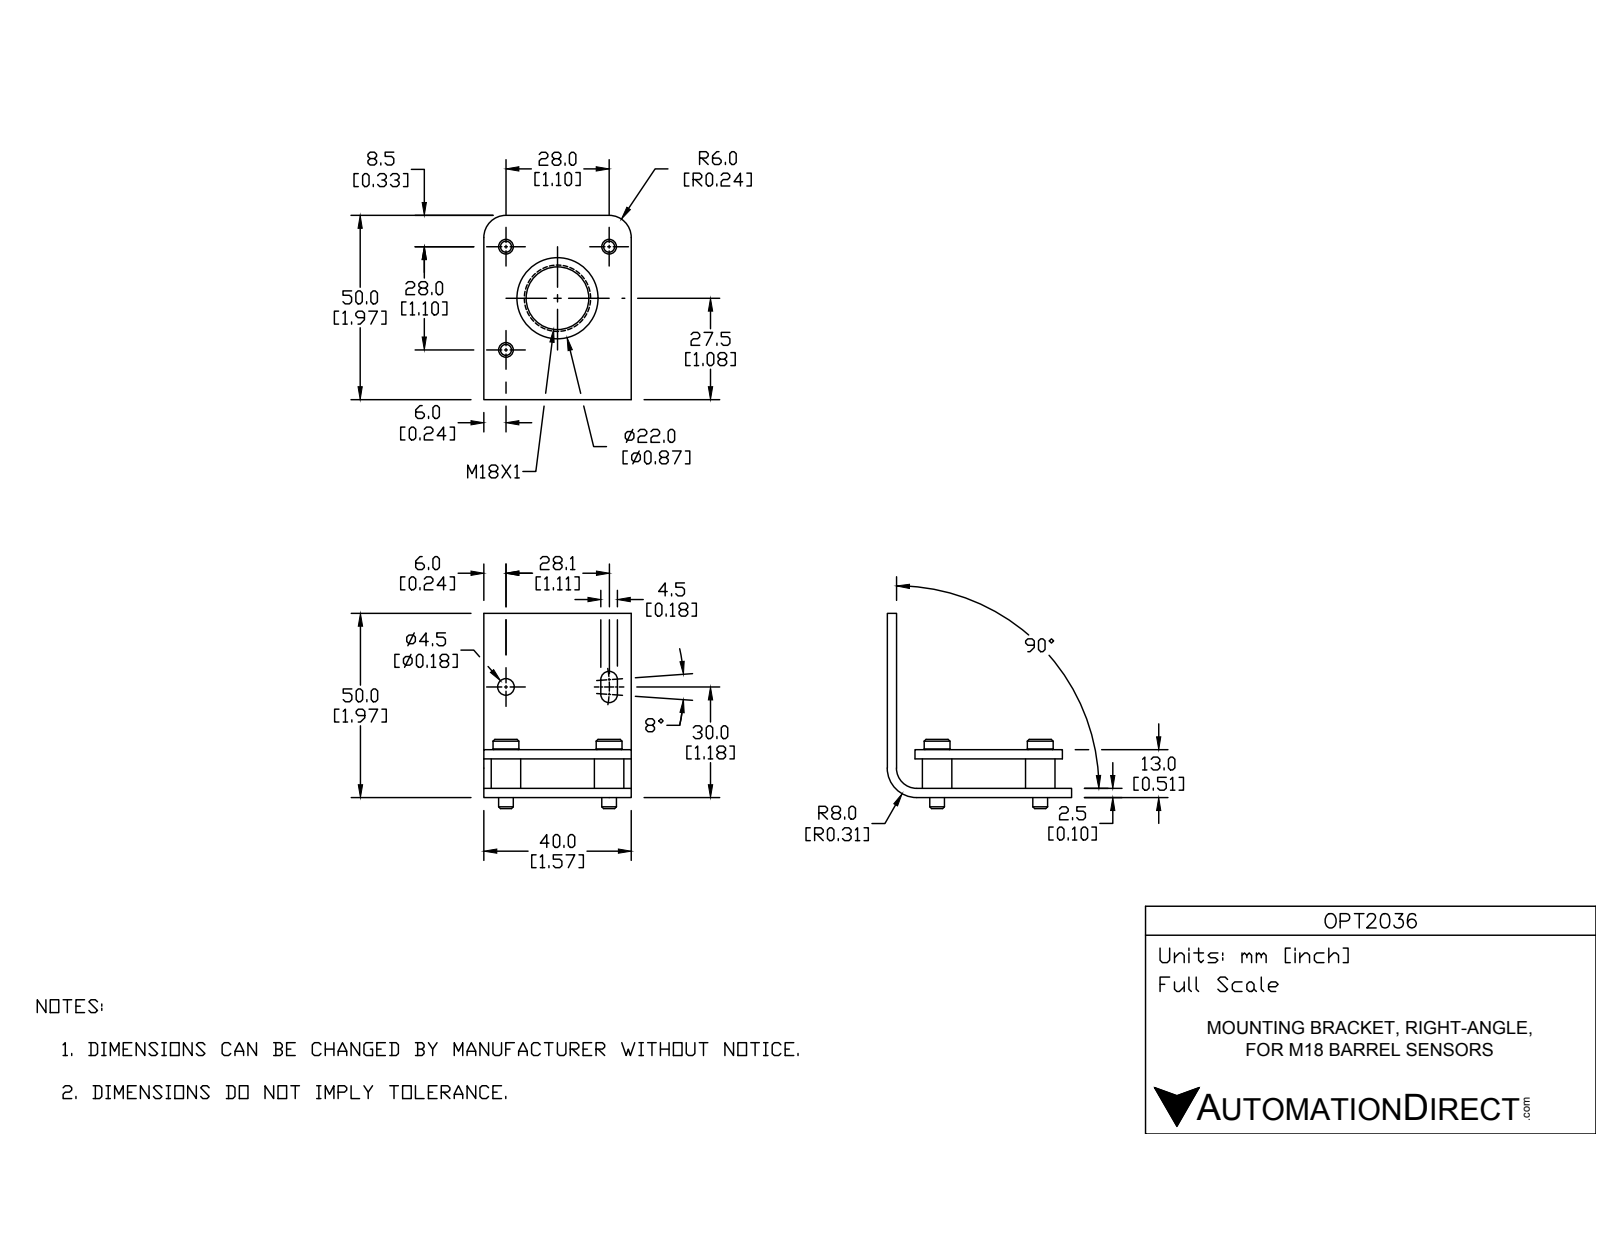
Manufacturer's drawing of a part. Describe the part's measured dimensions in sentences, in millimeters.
Its 3-D file was written by "Unknown (CONFIG_CONTROL_DESIGN)". It is 1 solid with 92 faces: 52 planar, 31 cylindrical and 9 other. Overall it measures 53 by 50 by 40 millimeters. Its volume is 12 991 cubic millimeters and its surface area 12 427 square millimeters. Round holes: 3 of diameter 4.3, 3 of diameter 5.6, 1 of diameter 4.5, 1 of diameter 17, 1 of diameter 22. Round bosses or shafts: 3 of diameter 8, 3 of diameter 7, 3 of diameter 4. Partial cylindrical surfaces (rounded edges, fillets, slot ends): 6 of radius 6, 2 of radius 2.25, 1 of radius 5.5, 1 of radius 8. The main face-to-face distances are 2.5, 10.5, 13, 8, 40, 47.5, 50, 39.5, 37, 7.5. The hole center spacings are 19.8, 28, 39.6.
